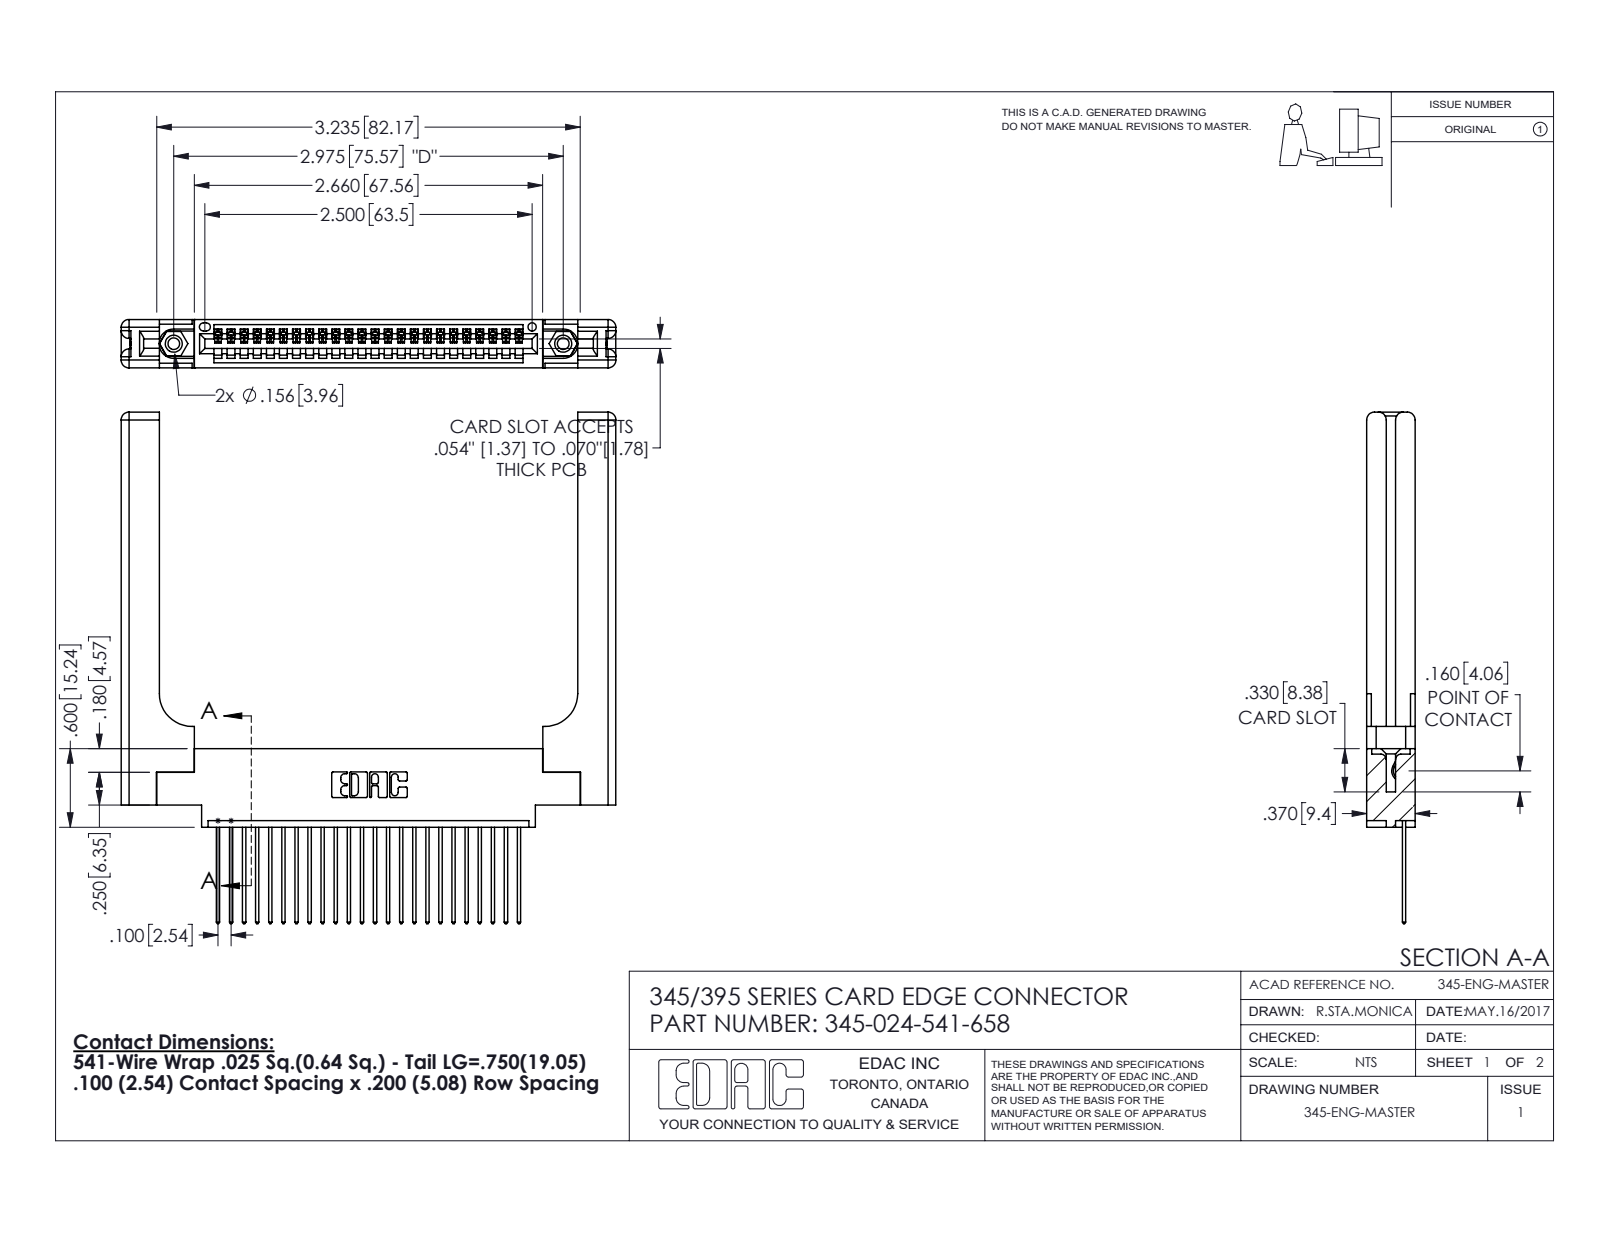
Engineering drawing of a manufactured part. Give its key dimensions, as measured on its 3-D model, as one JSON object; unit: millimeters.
{"part_name": "345-024-541-658; 345-220-058_345-220-058; 345-250-001_345-250-001-102; 345-292-001_345-293-141 (+1 more)", "step_written_by": "SolidWorks 2016 (CONFIG_CONTROL_DESIGN)", "units": "millimeters", "bodies": {"solids": 29, "faces": 1778, "planar": 1192, "cylindrical": 526, "other": 60}, "overall_size": [99.2, 96, 9.4], "volume_mm3": 17440, "surface_area_mm2": 17530, "round_holes": [[2.3, 2], [3.2, 2], [4, 2], [1.6, 1]], "round_bosses_or_shafts": [[3.9, 2]], "partial_cylinders_radius": [[0.2, 48], [0.3, 48], [0.3, 22], [1.5, 16], [0.2, 6], [0.8, 6], [0.7, 3], [0.8, 2]], "face_to_face_distances": [9.4, 1.8, 7.6, 2.5, 6.9, 0.6, 3.8, 3.8, 2, 5.1], "hole_center_spacings": [6.9, 69.6, 75.6]}
